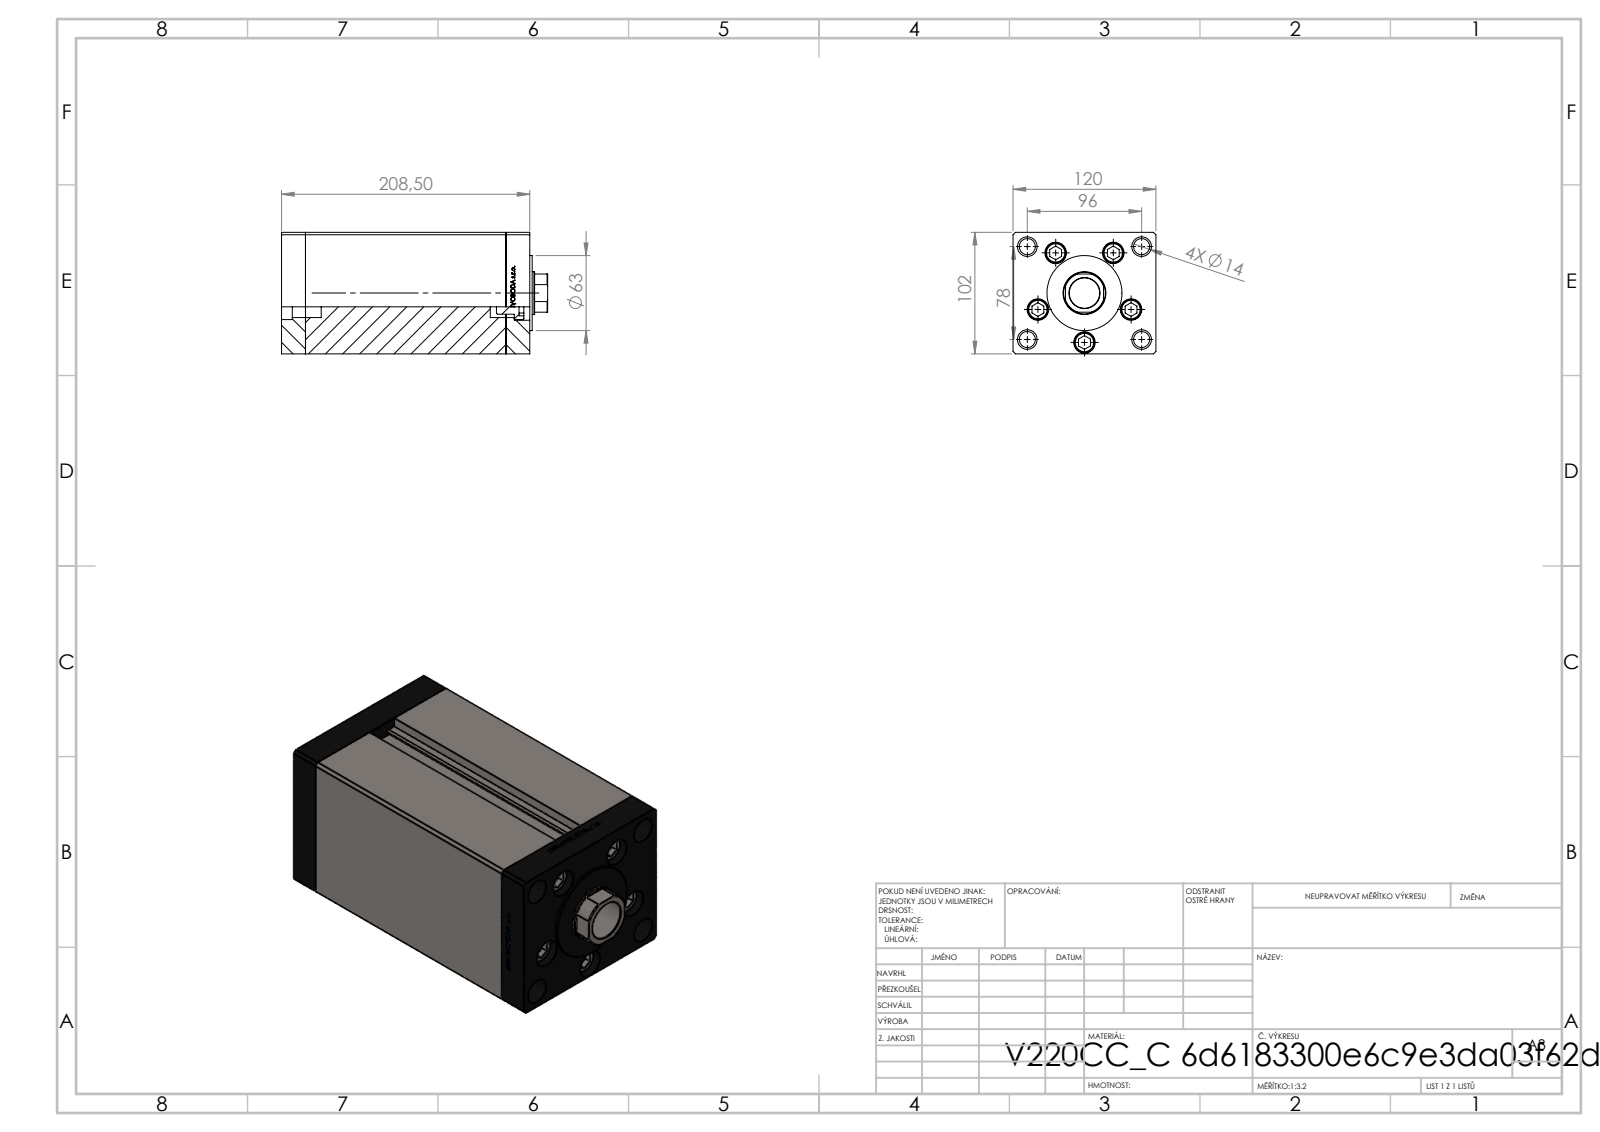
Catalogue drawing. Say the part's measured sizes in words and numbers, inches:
The part is named "V220C FRONT; V220C_VC_C; V220C_C MIDDLE; V220C BACK_C (+1 more)". Its 3-D file was written by "SolidWorks 2019 (CONFIG_CONTROL_DESIGN)". It is 13 solids with 1165 faces: 542 planar, 161 cylindrical and 462 other. Overall it measures 8.799 by 4.724 by 4.016 inches. Its volume is 130.7 cubic inches and its surface area 462.6 square inches. Round holes: 9 of diameter 0.531, 5 of diameter 0.709, 4 of diameter 0.472, 4 of diameter 0.65, 1 of diameter 0.669, 1 of diameter 1.004, 1 of diameter 1.417. Round bosses or shafts: 5 of diameter 0.315, 4 of diameter 0.669, 1 of diameter 2.48. Partial cylindrical surfaces (rounded edges, fillets, slot ends): 2 of radius 0.037, 1 of radius 0.689. The main face-to-face distances are 4.724, 4.016, 0.787, 6.634, 7.421, 1.348, 8.209, 6.86, 6.073, 0.561. The hole center spacings are 1.634, 2.435, 0.96, 1.051, 1.887, 1.893, 1.962, 2.109.
